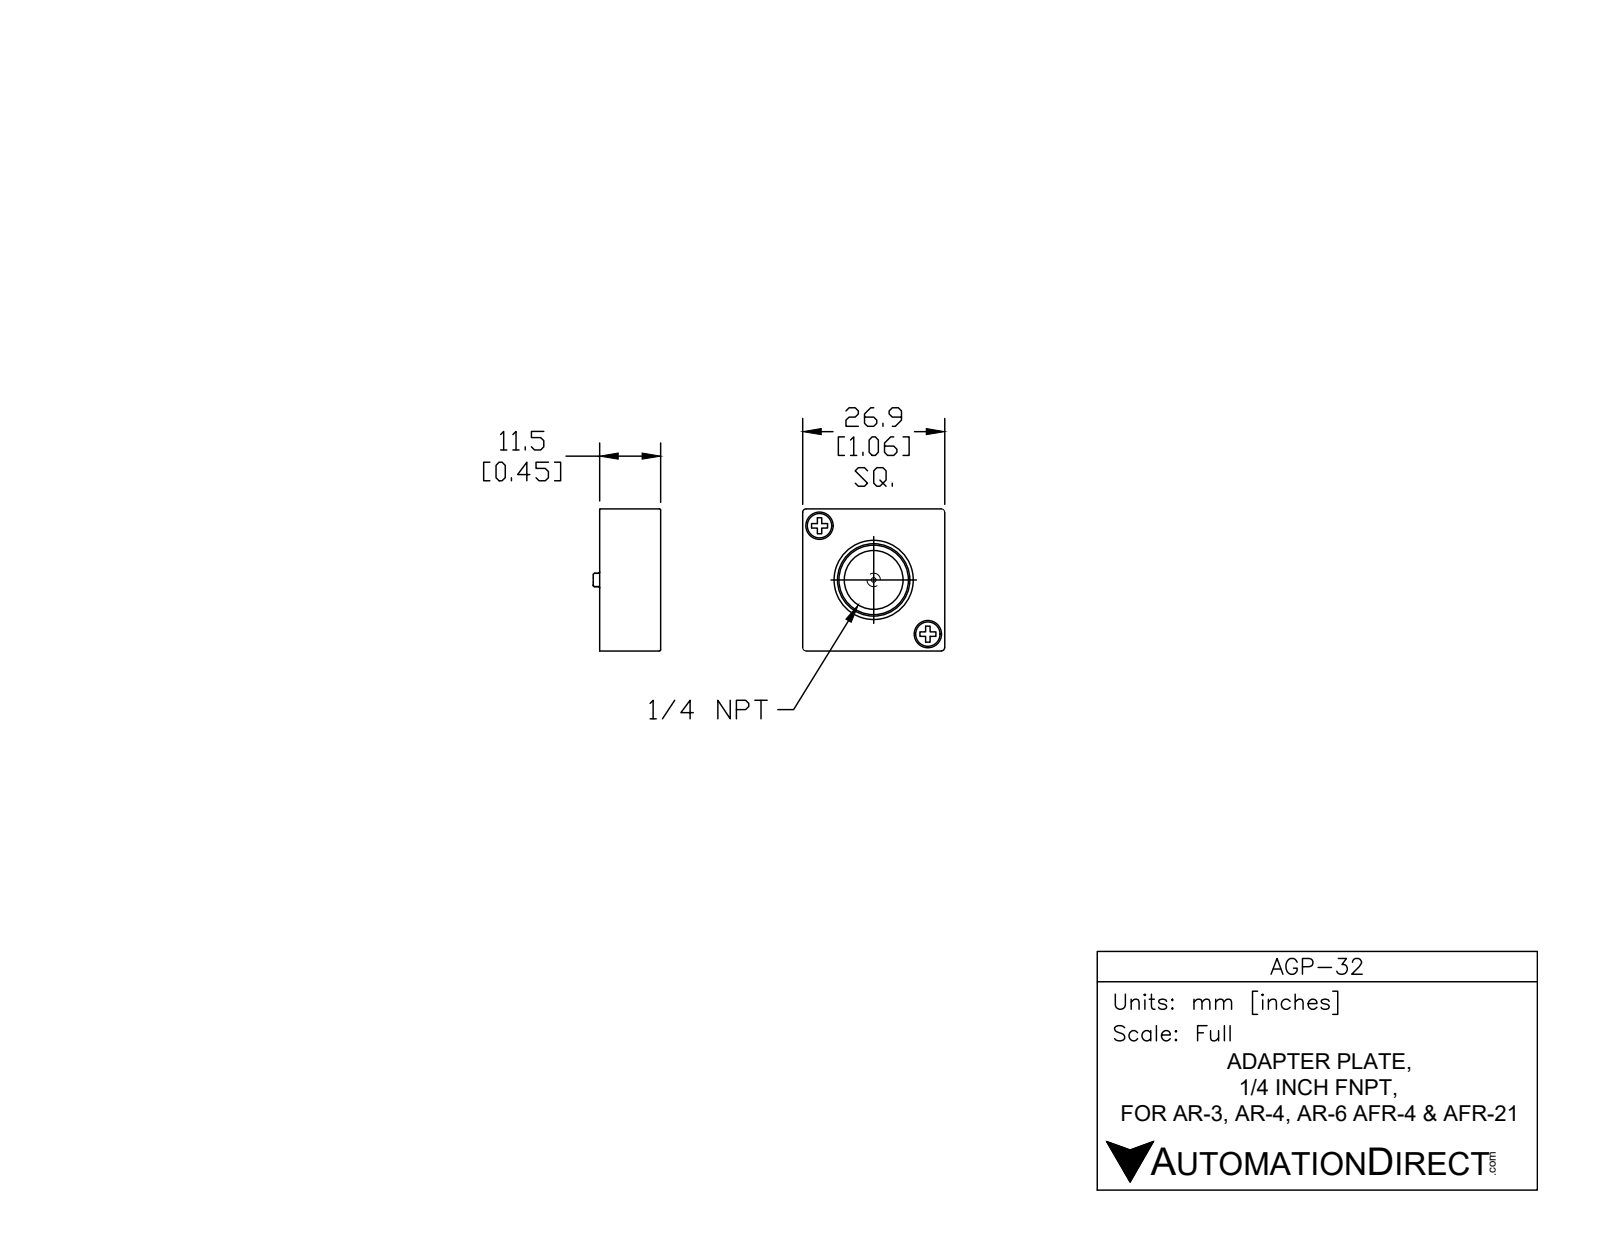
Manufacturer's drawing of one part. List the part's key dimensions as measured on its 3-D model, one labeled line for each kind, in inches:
Part name (STEP PRODUCT): AGP-32
STEP written by: SolidWorks 2015 (CONFIG_CONTROL_DESIGN)
Units: inches
Bodies: 1 solid, 73 faces (39 planar, 22 cylindrical, 12 other)
Overall size (bounding box): 1.058 × 1.058 × 0.502
Volume: 0.416 in³ · Surface area: 5.048 in²
Round holes (diameter × count): ⌀0.203 ×2, ⌀0.035 ×1, ⌀0.438 ×1
Round bosses / shafts (diameter × count): ⌀0.181 ×2, ⌀0.1 ×1
Partial cylindrical surfaces — rounded edges, fillets, slot ends (radius × count): R0.01 ×4, R0.025 ×4
Main face-to-face distances: 1.058, 0.454, 0.054, 0.4, 0.39, 0.064, 0.424, 0.37, 0.36, 0.03
Hole centre spacings: 0.571, 1.141
